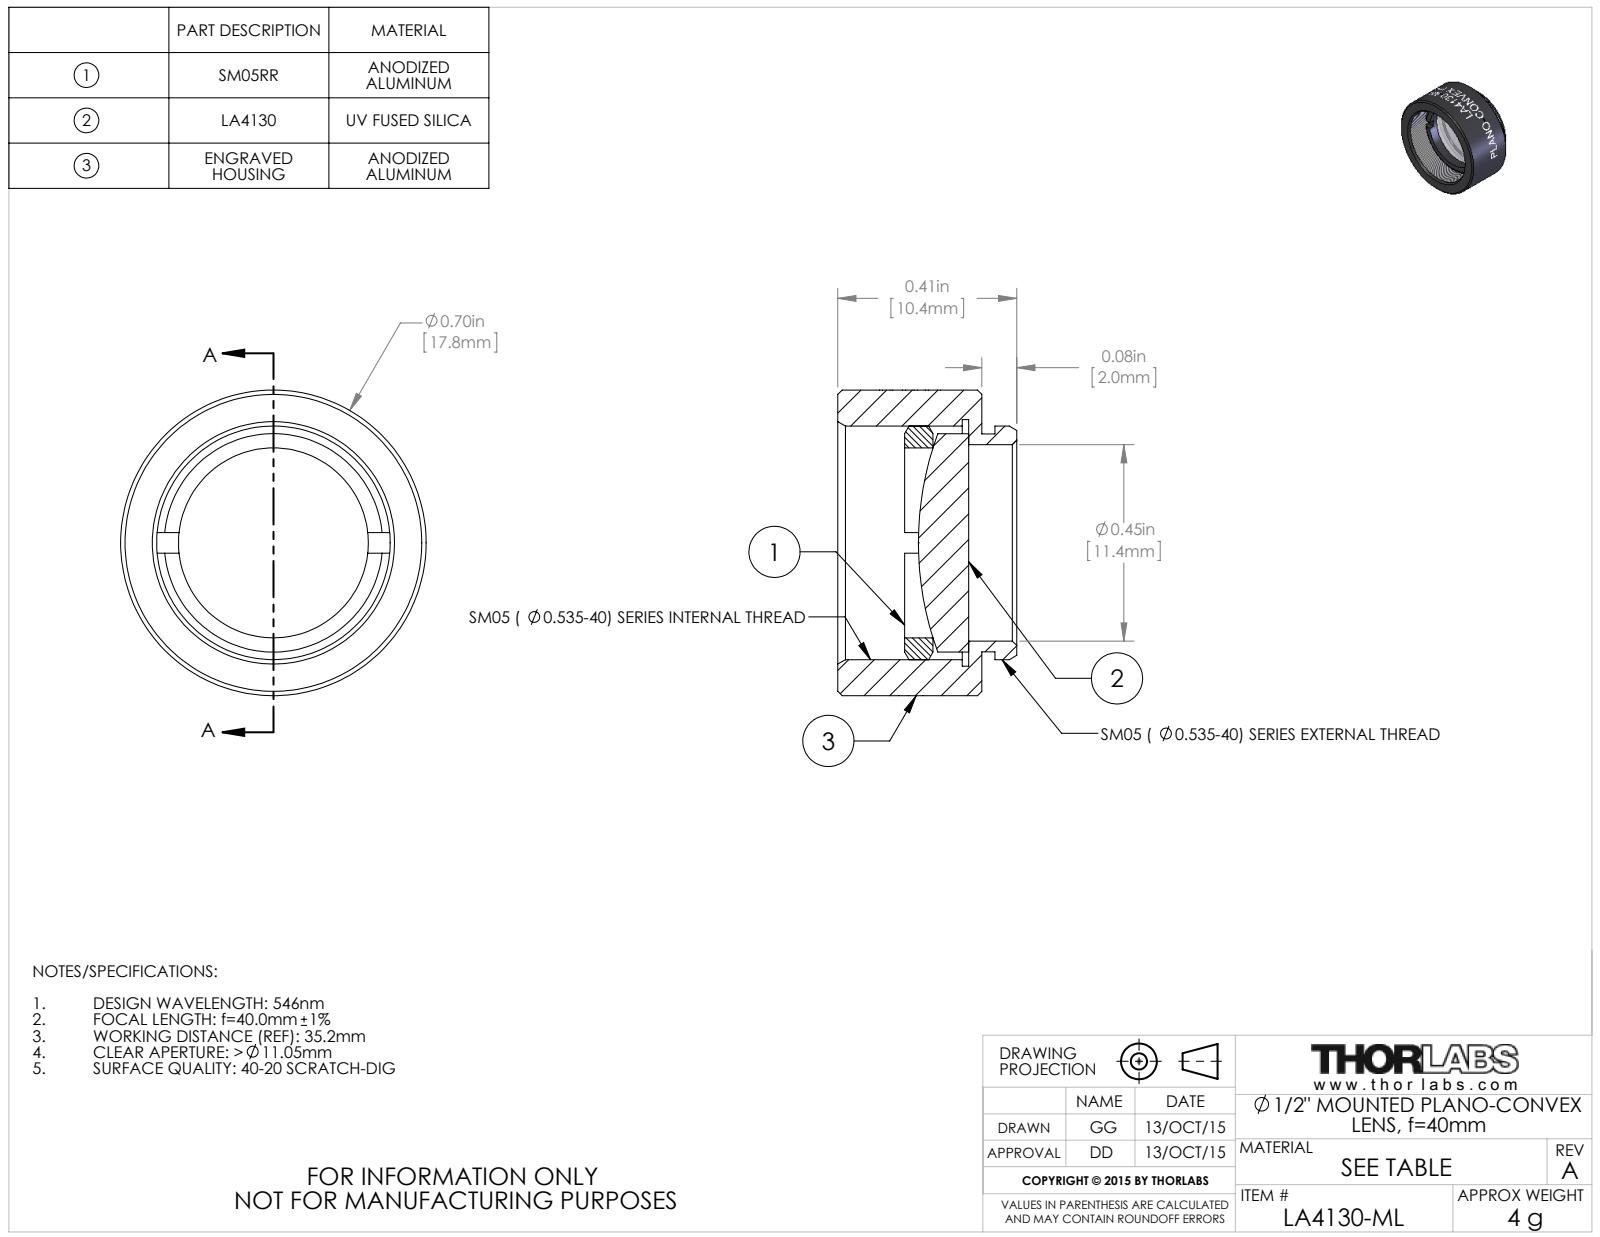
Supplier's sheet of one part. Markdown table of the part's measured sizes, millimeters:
| quantity | value |
| --- | --- |
| part name | TTN039159-E0W |
| STEP written by | SolidWorks 2014 (CONFIG_CONTROL_DESIGN) |
| units | millimeters |
| bodies | 3 solids, 107 faces (16 planar, 74 cylindrical, 17 other) |
| overall size | 17.78 × 17.78 × 10.41 |
| volume | 1 328 mm³ |
| surface area | 1 844 mm² |
| round holes (diameter × count) | 11.05 × 1, 11.43 × 1, 13.59 × 1, 14.35 × 1 |
| round bosses / shafts (diameter × count) | 17.78 × 1, 13.59 × 1, 12.7 × 1, 12.67 × 1 |
| main face-to-face distances | 0.76, 8.38, 7.62, 2.85, 2.09, 5.53, 4.5, 3.74, 1.65, 3.88 |
